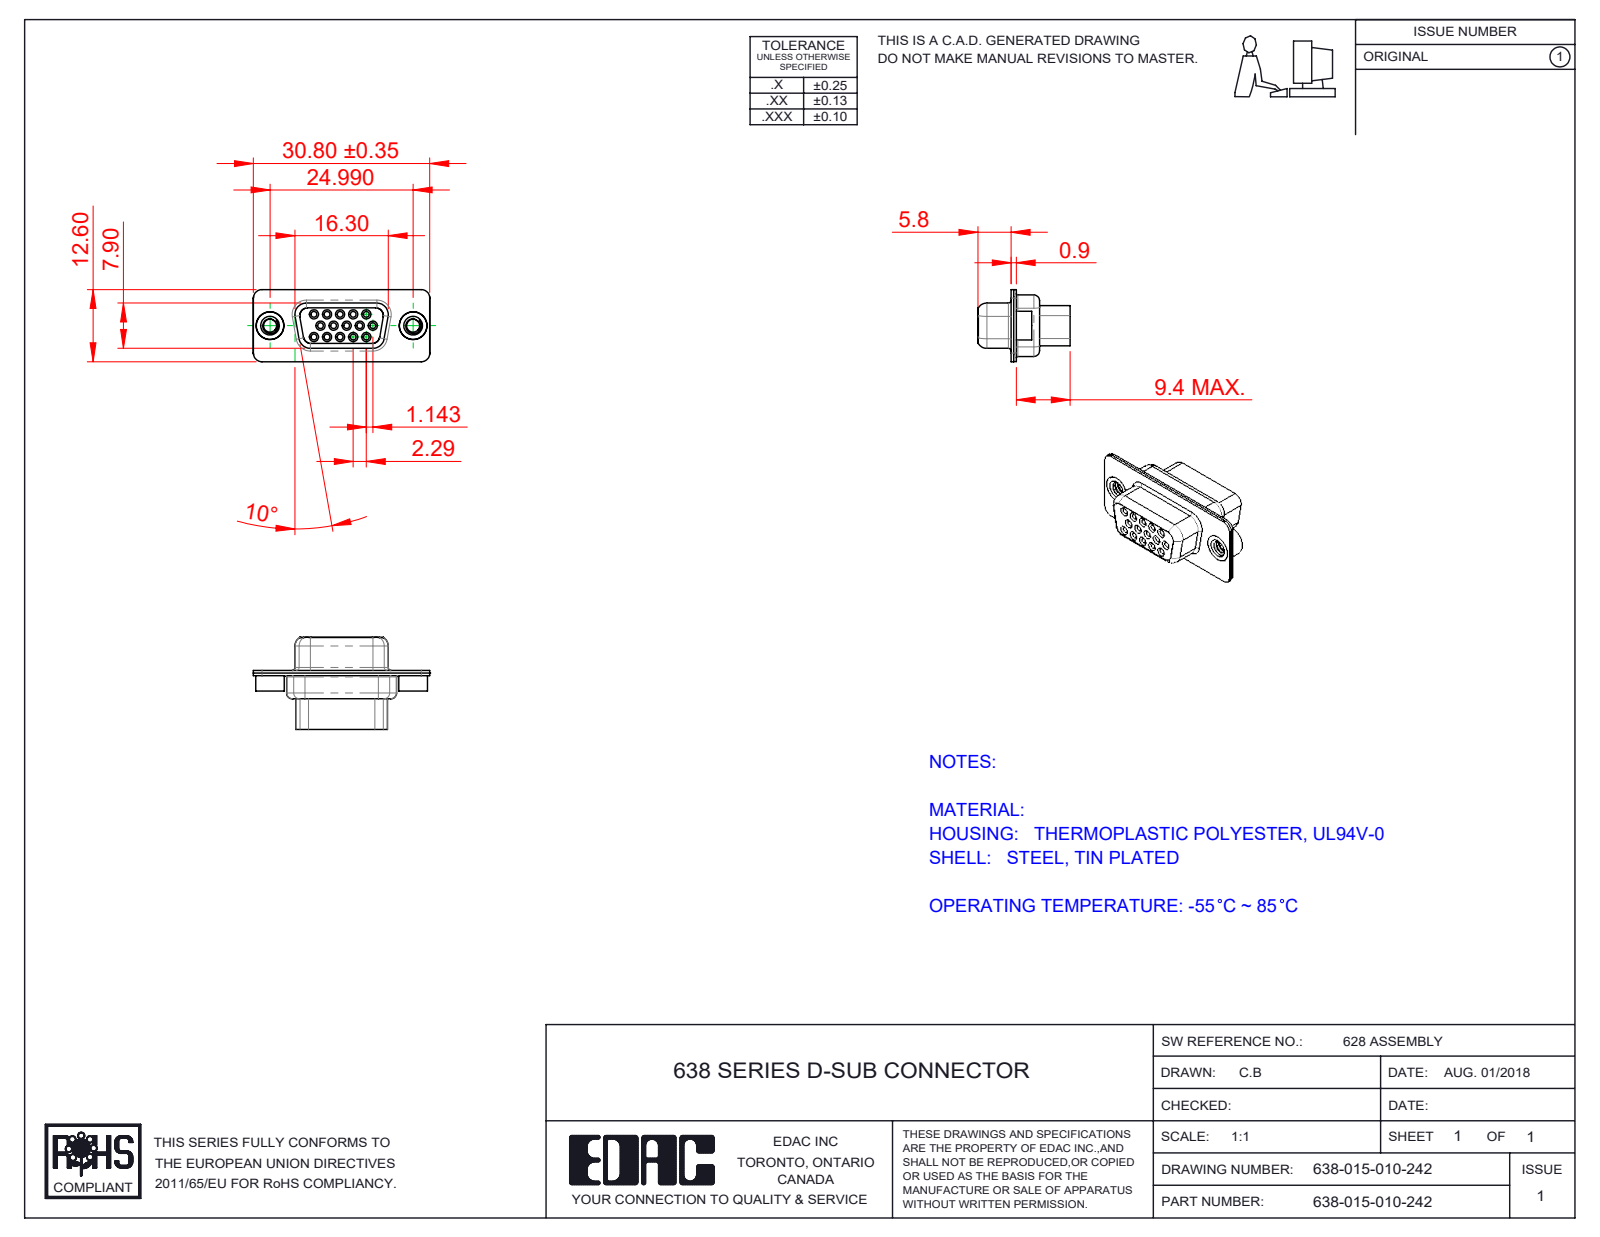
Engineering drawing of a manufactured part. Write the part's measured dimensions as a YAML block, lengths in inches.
part_name: "638-015-010-242; 638 4-40 Threaded Rivet; 638 Housing_15 Contacts HP; 638 Shell Front_15 Contacts (+1 more)"
step_written_by: "SolidWorks 2020 (CONFIG_CONTROL_DESIGN)"
units: inches
bodies: {solids: 5, faces: 474, planar: 112, cylindrical: 257, other: 105}
overall_size: [1.213, 0.634, 0.496]
volume: 0.104
surface_area: 7.053
round_holes:
  - {diameter: 0.039, count: 15}
  - {diameter: 0.067, count: 15}
  - {diameter: 0.071, count: 15}
  - {diameter: 0.079, count: 15}
  - {diameter: 0.089, count: 2}
  - {diameter: 0.157, count: 2}
  - {diameter: 0.159, count: 2}
  - {diameter: 0.191, count: 2}
round_bosses_or_shafts:
  - {diameter: 0.197, count: 2}
  - {diameter: 0.195, count: 2}
  - {diameter: 0.189, count: 2}
partial_cylinders:
  - {radius: 0.059, count: 20}
  - {radius: 0.079, count: 12}
  - {radius: 0.061, count: 8}
  - {radius: 0.053, count: 5}
  - {radius: 0.01, count: 4}
  - {radius: 0.02, count: 4}
  - {radius: 0.022, count: 4}
  - {radius: 0.028, count: 4}
face_to_face_distances: [0.018, 0.035, 0.016, 0.056, 0.35, 0.26, 0.37, 0.276, 0.244, 0.055]
hole_center_spacings: [0.156, 0.09, 0.18, 0.09, 0.238, 0.27, 0.312, 0.238]
